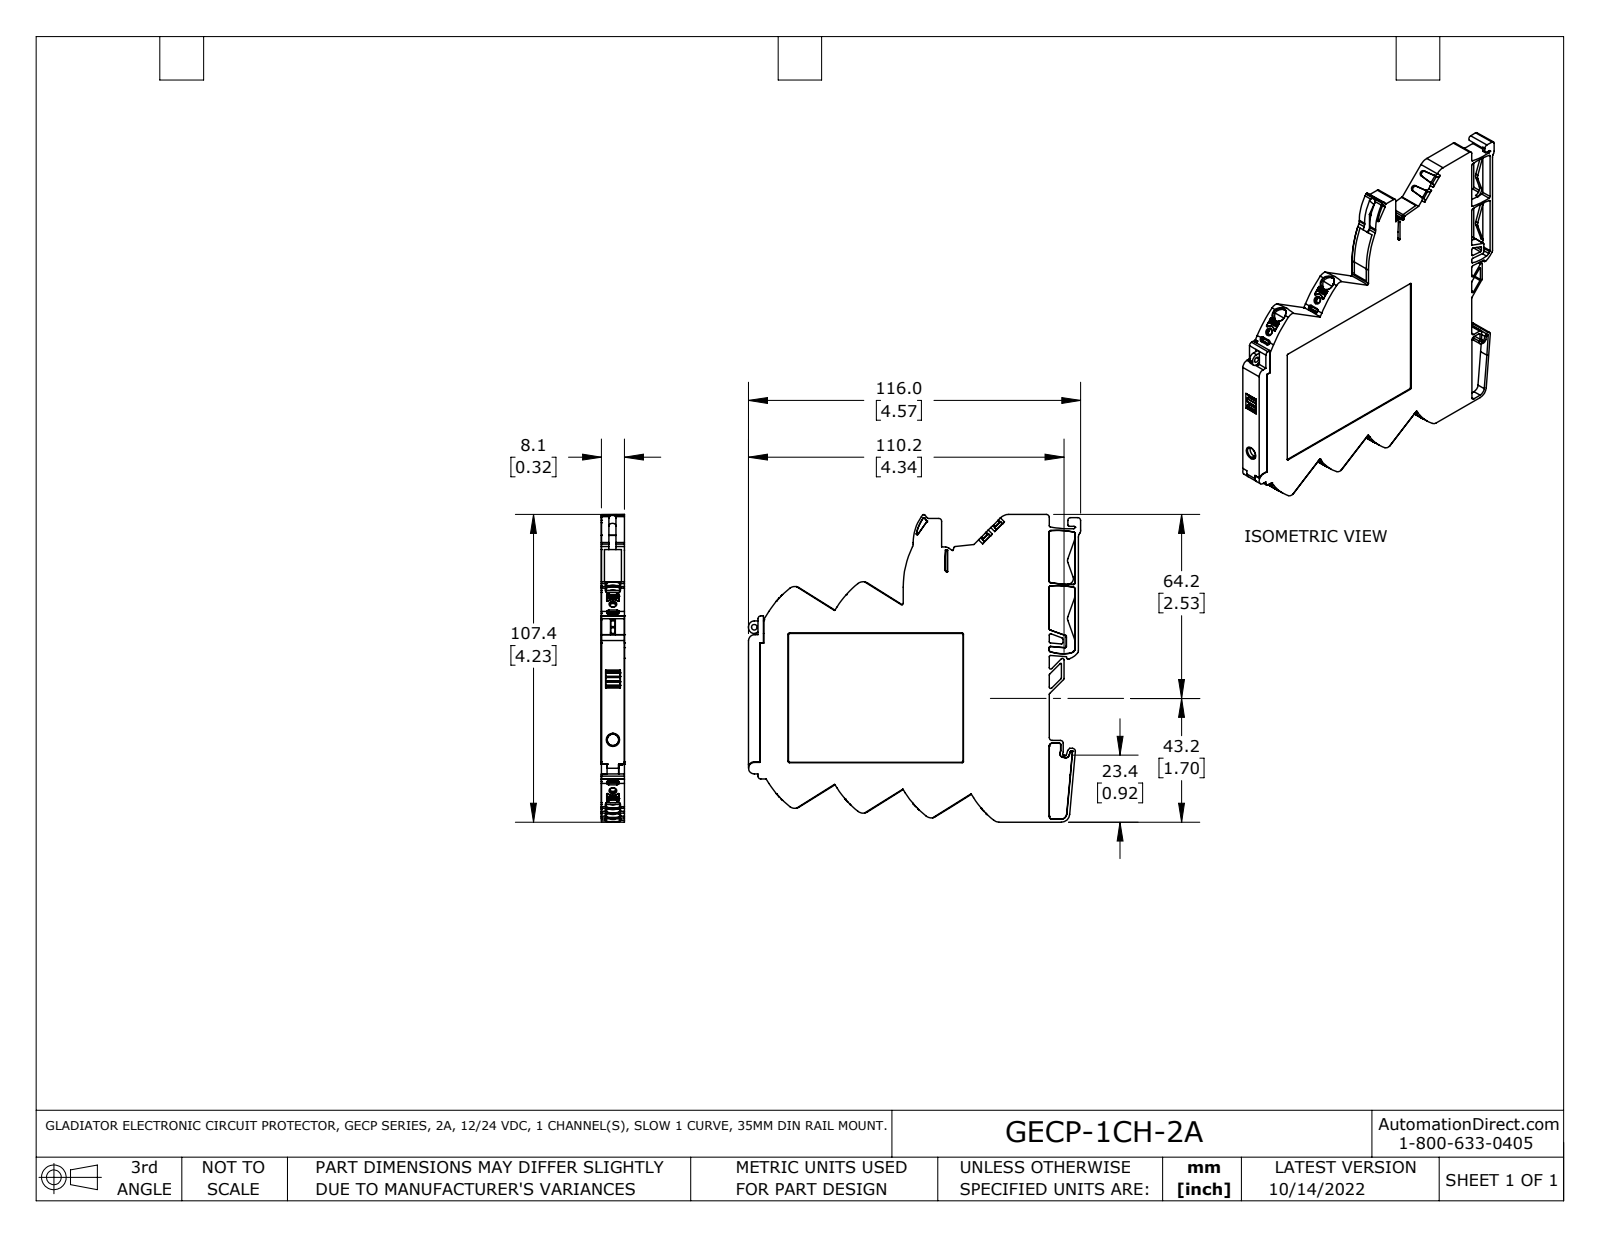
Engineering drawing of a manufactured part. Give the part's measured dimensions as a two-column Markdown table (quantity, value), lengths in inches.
| quantity | value |
| --- | --- |
| part name | GECP-1CH-2A |
| STEP written by | SolidWorks 2021 (AUTOMOTIVE_DESIGN) |
| units | inches |
| bodies | 1 solid, 1182 faces (549 planar, 466 cylindrical, 167 other) |
| overall size | 4.567 × 4.241 × 0.319 |
| volume | 4.341 in³ |
| surface area | 46.72 in² |
| round holes (diameter × count) | 0.083 × 6, 0.078 × 1, 0.087 × 1 |
| round bosses / shafts (diameter × count) | 0.083 × 1 |
| partial cylindrical surfaces (radius × count) | 0.02 × 58, 0.039 × 45, 0.008 × 43, 0.01 × 28, 0.012 × 27, 0.079 × 13, 0.009 × 12, 1.299 × 12 |
| main face-to-face distances | 0.319, 0.311, 0.309, 0.317, 0.201, 0.157, 0.118, 0.354, 3.935, 4.093 |
| hole center spacings | 0.559, 1.118, 0.559, 1.677, 1.937 |
